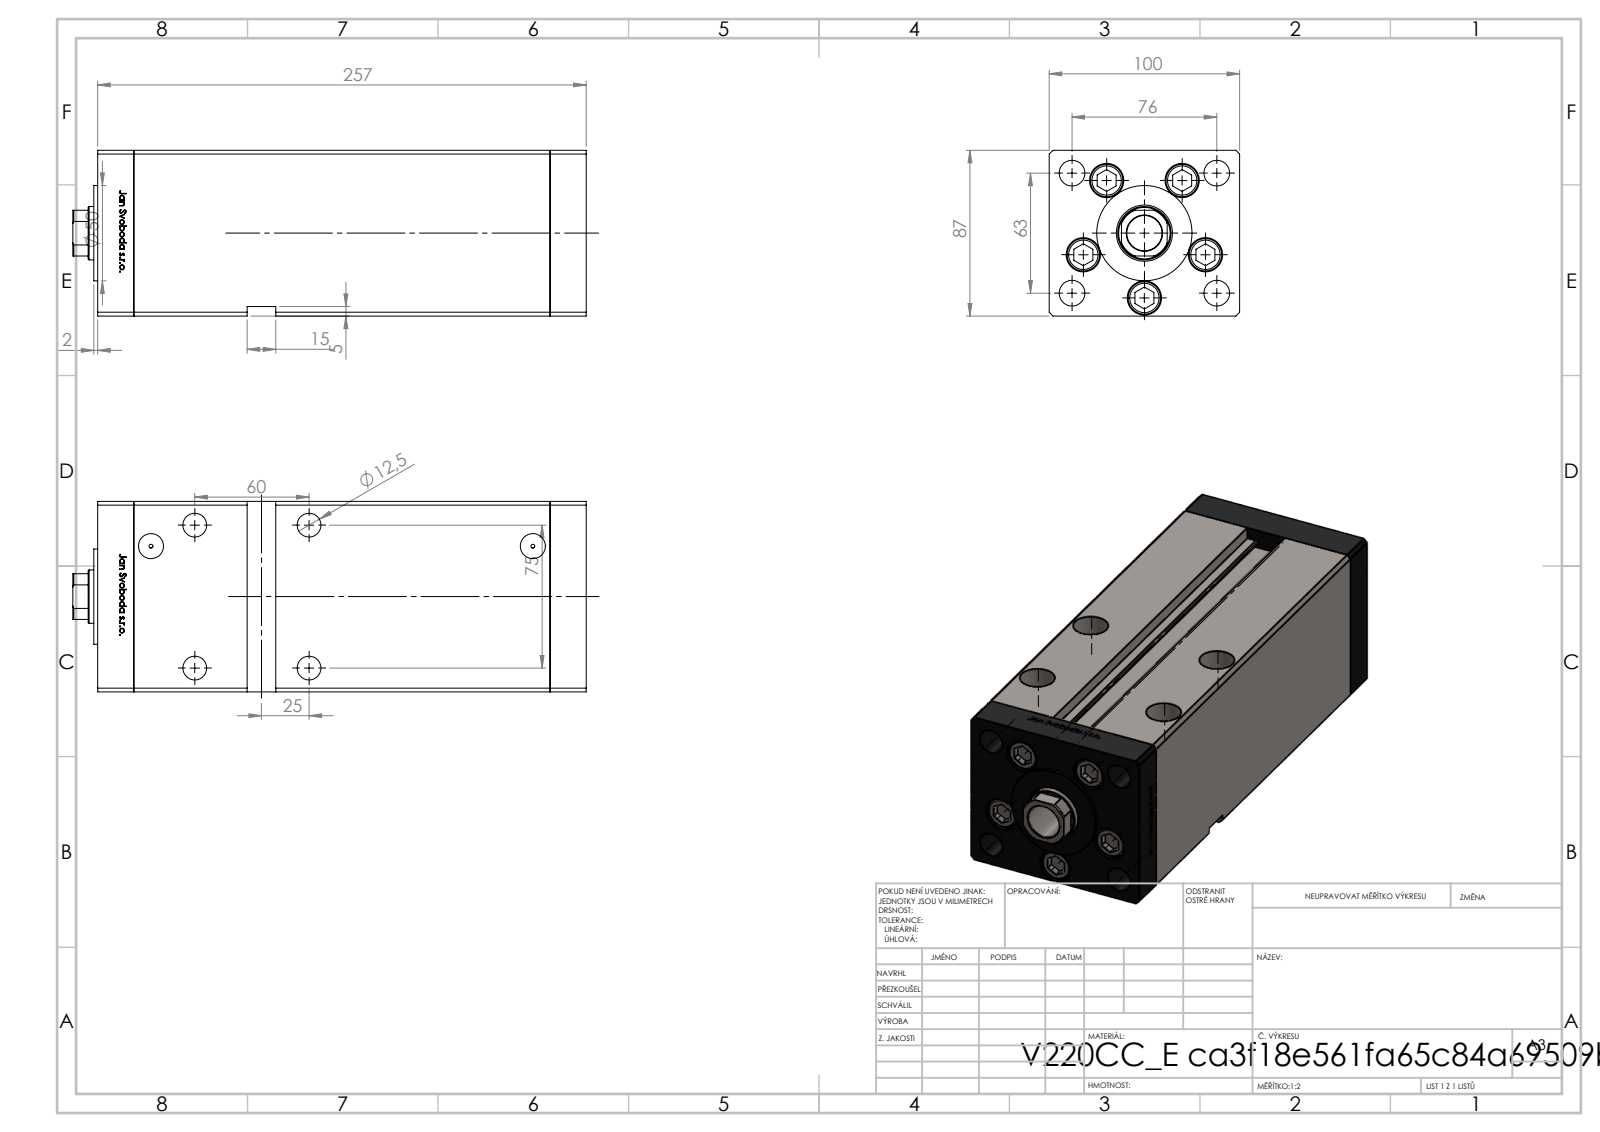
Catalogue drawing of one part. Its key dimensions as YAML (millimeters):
part_name: "V220C_FRONT_E; V220C BACK_E; V220C_VC_E; ALLEN BOLT (+1 more)"
step_written_by: "SolidWorks 2019 (CONFIG_CONTROL_DESIGN)"
units: millimeters
bodies: {solids: 14, faces: 1214, planar: 475, cylindrical: 165, other: 574}
overall_size: [269.5, 100, 87]
volume: 1865000
surface_area: 265760
round_holes:
  - {diameter: 13.5, count: 11}
  - {diameter: 18, count: 5}
  - {diameter: 18.5, count: 5}
  - {diameter: 12.5, count: 4}
  - {diameter: 2, count: 2}
  - {diameter: 13.16, count: 2}
  - {diameter: 28, count: 1}
  - {diameter: 29.5, count: 1}
round_bosses_or_shafts:
  - {diameter: 17, count: 5}
  - {diameter: 8, count: 5}
  - {diameter: 50, count: 1}
partial_cylinders:
  - {radius: 0.93, count: 2}
  - {radius: 13.5, count: 1}
face_to_face_distances: [100, 87, 19, 218.5, 237.5, 34.25, 256.5, 15.25, 203.25, 222.25]
hole_center_spacings: [34, 18.59, 39.64, 49.36, 57.95, 21.03, 38.08, 39.27]
